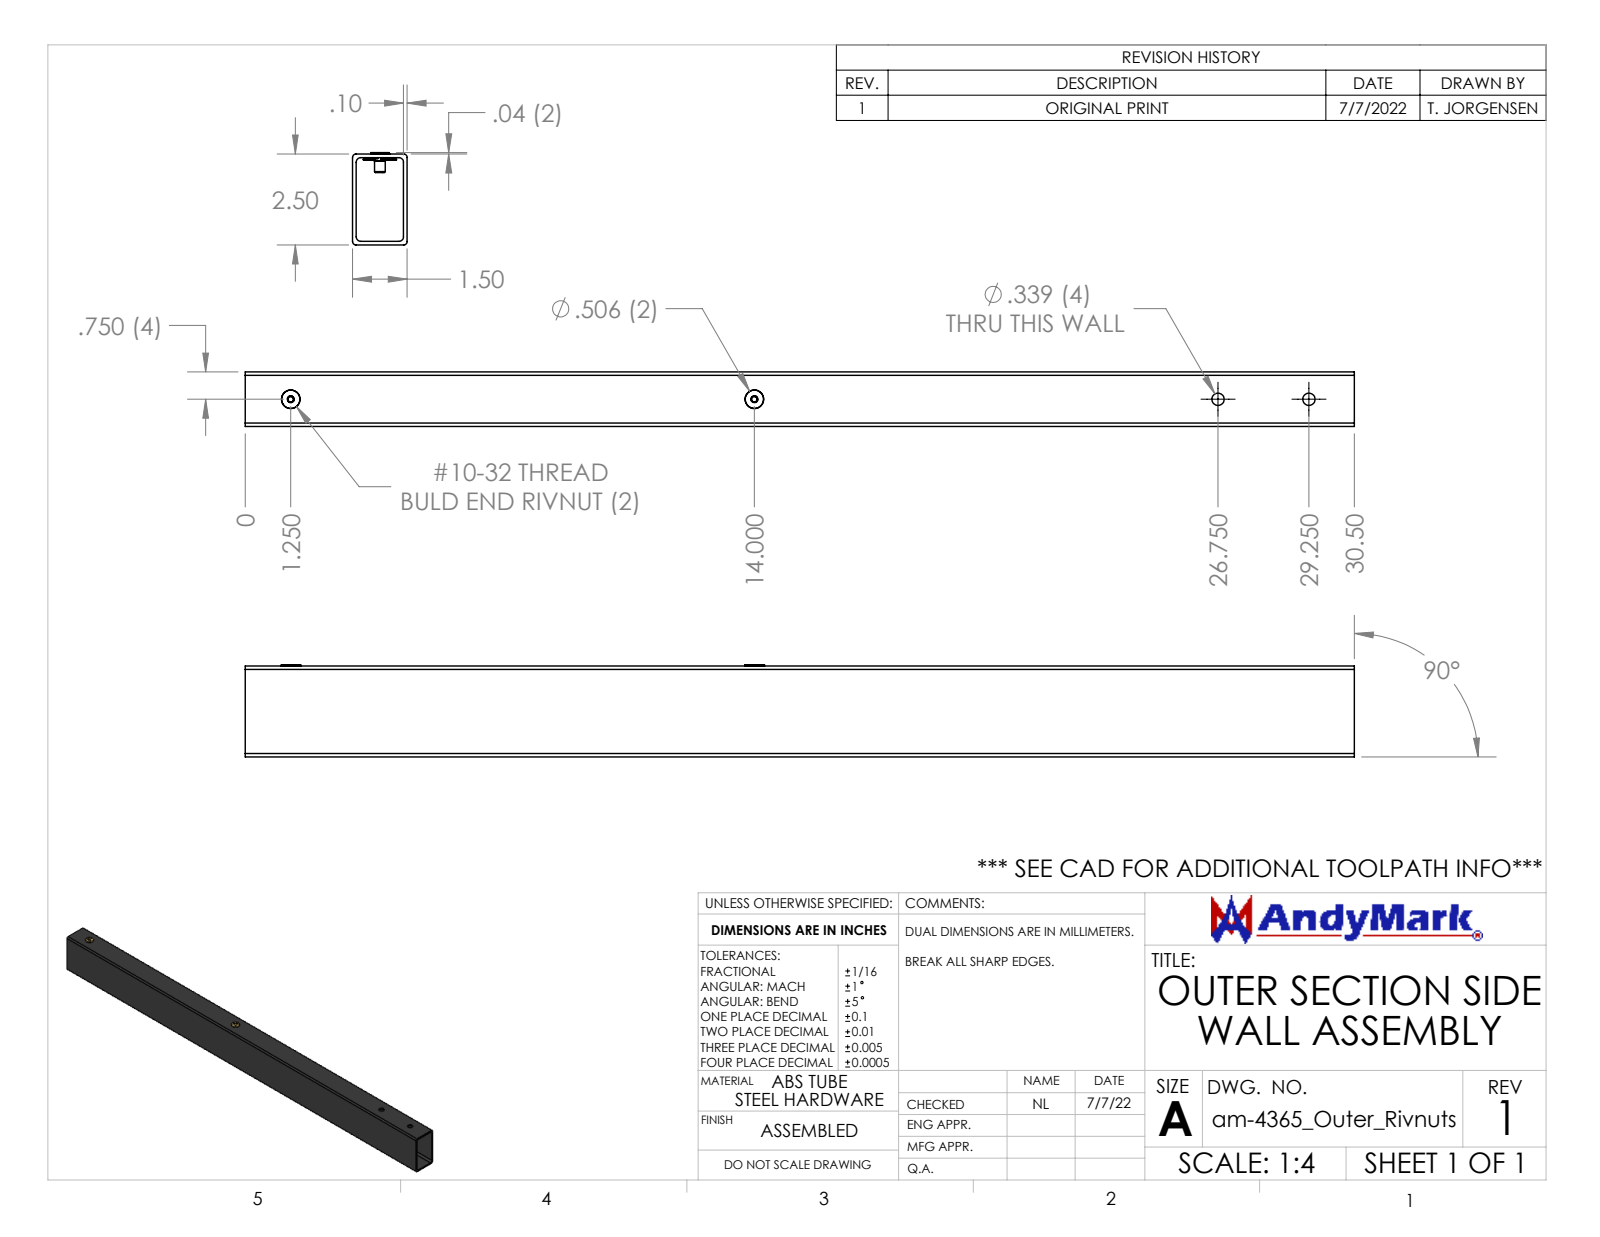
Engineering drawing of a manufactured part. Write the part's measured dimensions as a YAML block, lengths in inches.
part_name: "am-1577 10-32 RivNut for Plastics_Installed; am-4365_Outer_Rivnuts Outer Section Side Wall; ip-4365_Outer_Drilled Outer Section Side Wall"
step_written_by: "SolidWorks 2022 (CONFIG_CONTROL_DESIGN)"
units: inches
bodies: {solids: 3, faces: 226, planar: 66, cylindrical: 80, other: 80}
overall_size: [30.5, 2.538, 1.5]
volume: 23.4
surface_area: 458.1
round_holes:
  - {diameter: 0.339, count: 4}
  - {diameter: 0.19, count: 2}
round_bosses_or_shafts:
  - {diameter: 0.51, count: 2}
  - {diameter: 0.358, count: 2}
  - {diameter: 0.296, count: 2}
partial_cylinders:
  - {radius: 0.094, count: 4}
  - {radius: 0.125, count: 4}
face_to_face_distances: [0.1, 1.4, 1.5, 2.4, 1.3, 2.5, 2.3, 30.5, 0.038, 0.138]
hole_center_spacings: [12.75, 2.5, 15.25, 25.5, 28]
